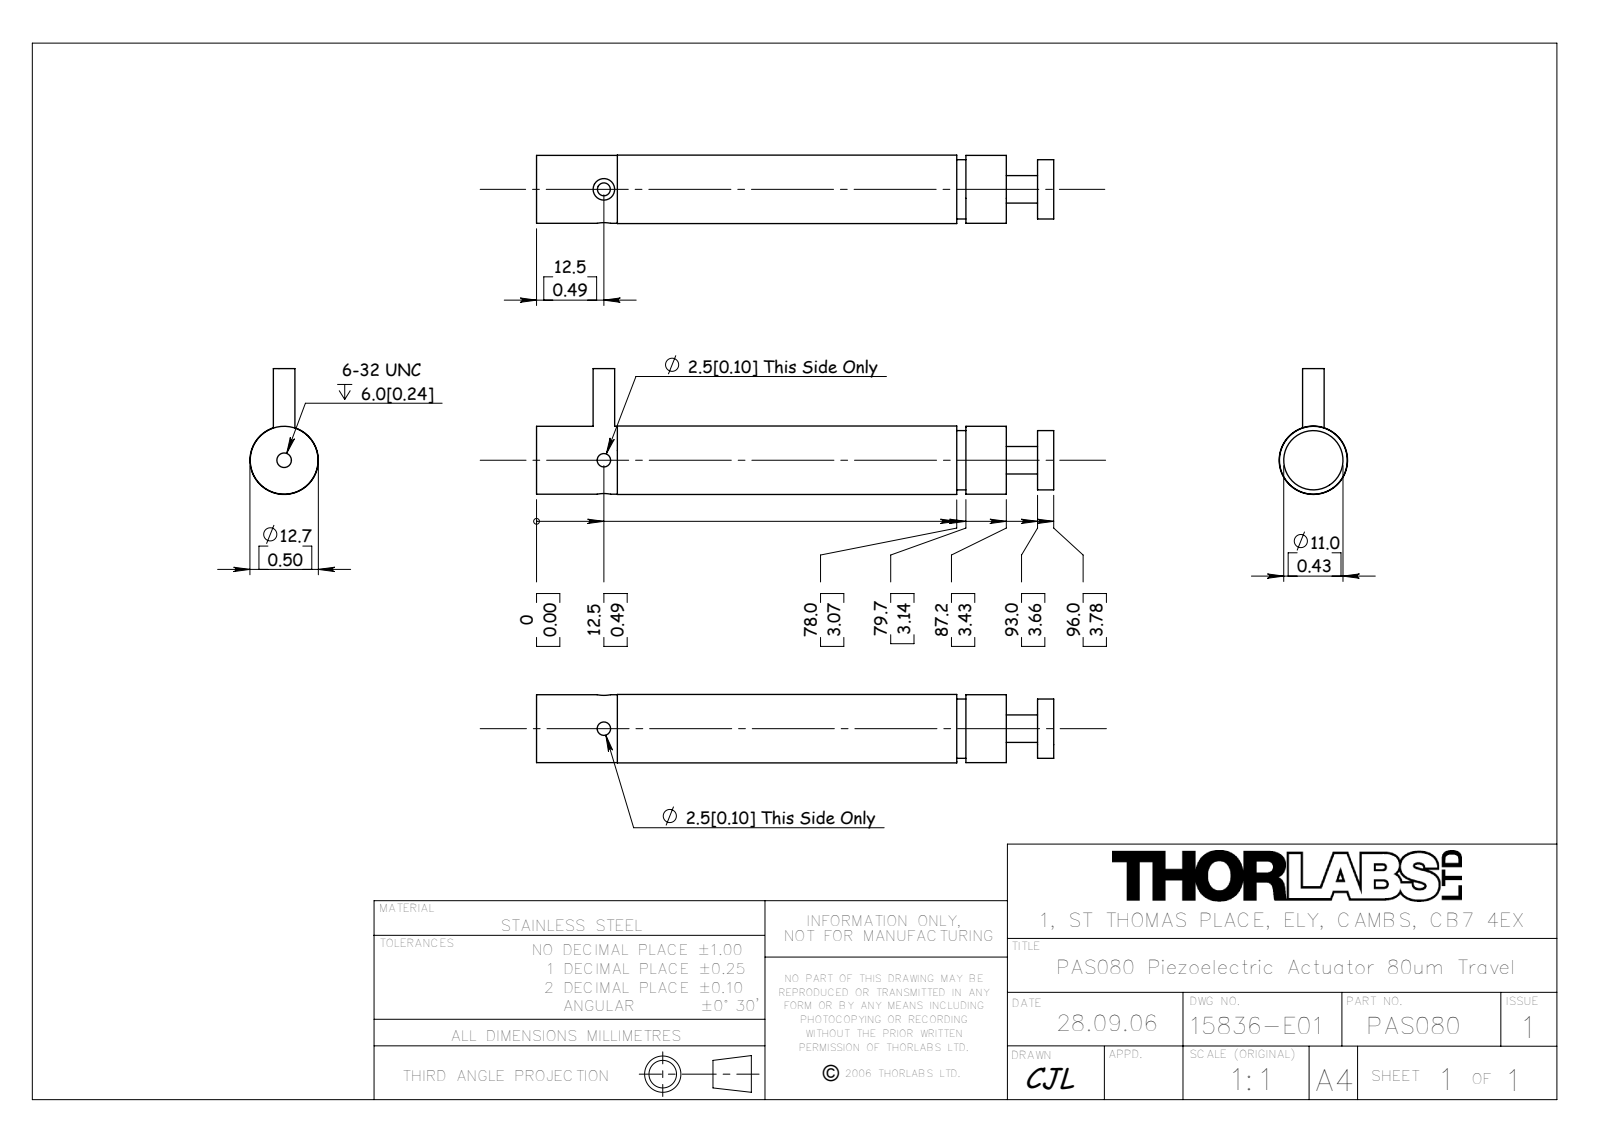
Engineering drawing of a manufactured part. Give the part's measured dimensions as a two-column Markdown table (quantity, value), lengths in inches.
| quantity | value |
| --- | --- |
| part name | 15836-E0W |
| STEP written by | SolidWorks 2007 (AUTOMOTIVE_DESIGN) |
| units | inches |
| bodies | 0 solids, 39 faces (11 planar, 28 cylindrical, 0 other) |
| overall size | 3.78 × 0.919 × 0.5 |
| round holes (diameter × count) | 0.098 × 2, 0.094 × 1, 0.107 × 1, 0.209 × 1, 0.376 × 1, 0.449 × 1 |
| round bosses / shafts (diameter × count) | 0.5 × 1, 0.496 × 1, 0.433 × 1, 0.201 × 1, 0.157 × 1 |
| main face-to-face distances | 3.433, 0.346, 3.78, 0.118, 0.228, 3.661, 0.591, 3.071, 3.386, 3.268 |
